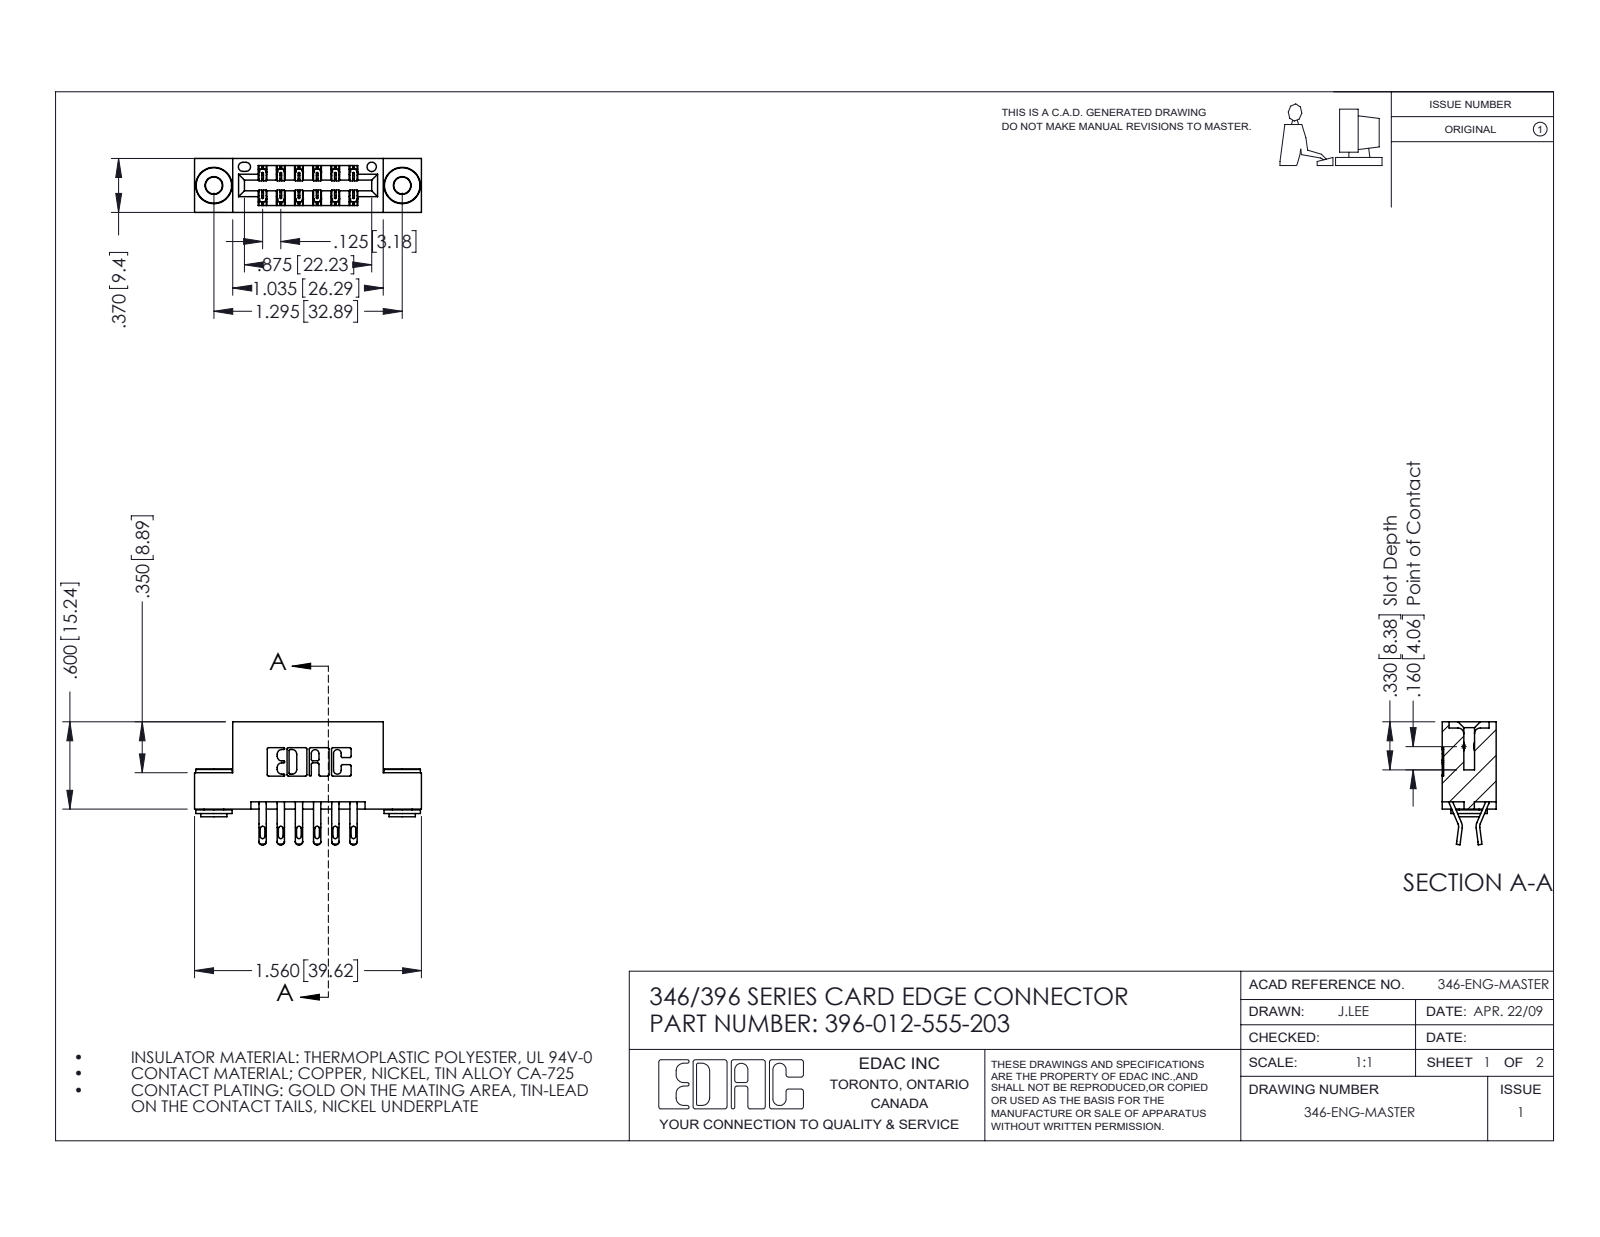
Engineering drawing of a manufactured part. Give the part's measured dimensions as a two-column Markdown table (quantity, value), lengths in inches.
| quantity | value |
| --- | --- |
| part name | 345-250-002_345-250-002-102; 346 Part_Flush Mounting Lugs - 0.156 Dia-TH; 345-292-001_555 Tail; 396-012-555-203 |
| STEP written by | SolidWorks 2016 (CONFIG_CONTROL_DESIGN) |
| units | inches |
| bodies | 15 solids, 856 faces (482 planar, 366 cylindrical, 8 other) |
| overall size | 1.56 × 0.845 × 0.37 |
| volume | 0.222 in³ |
| surface area | 7.399 in² |
| round holes (diameter × count) | 0.116 × 2, 0.156 × 2, 0.064 × 1 |
| round bosses / shafts (diameter × count) | 0.25 × 2, 0.18 × 2, 0.136 × 2 |
| partial cylindrical surfaces (radius × count) | 0.016 × 24, 0.02 × 24, 0.01 × 22, 0.006 × 18, 0.007 × 6, 0.031 × 6, 0.026 × 3, 0.01 × 2 |
| main face-to-face distances | 0.25, 0.37, 0.048, 0.322, 0.025, 0.125, 0.148, 0.222, 0.1, 0.174 |
| hole center spacings | 0.246, 1.092, 1.295 |
